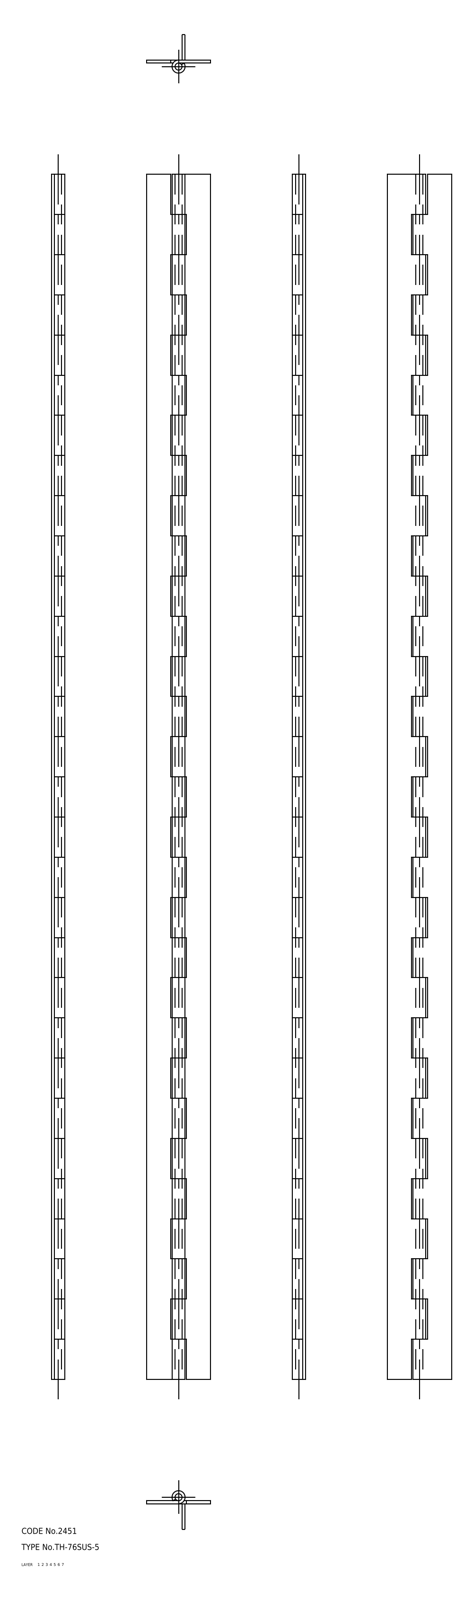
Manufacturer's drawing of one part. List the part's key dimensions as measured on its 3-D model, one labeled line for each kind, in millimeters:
Part name (STEP PRODUCT): shaft; hinge piece_B; hinge piece_A; TH_76SUS_5_15639_36
STEP written by: CADfix (AUTOMOTIVE_DESIGN)
Units: millimetres
Bodies: 3 solids, 192 faces (0 planar, 0 cylindrical, 192 other)
Overall size (bounding box): 600 × 32 × 6.5
Volume: 42 827 mm³ · Surface area: 61 229 mm²
